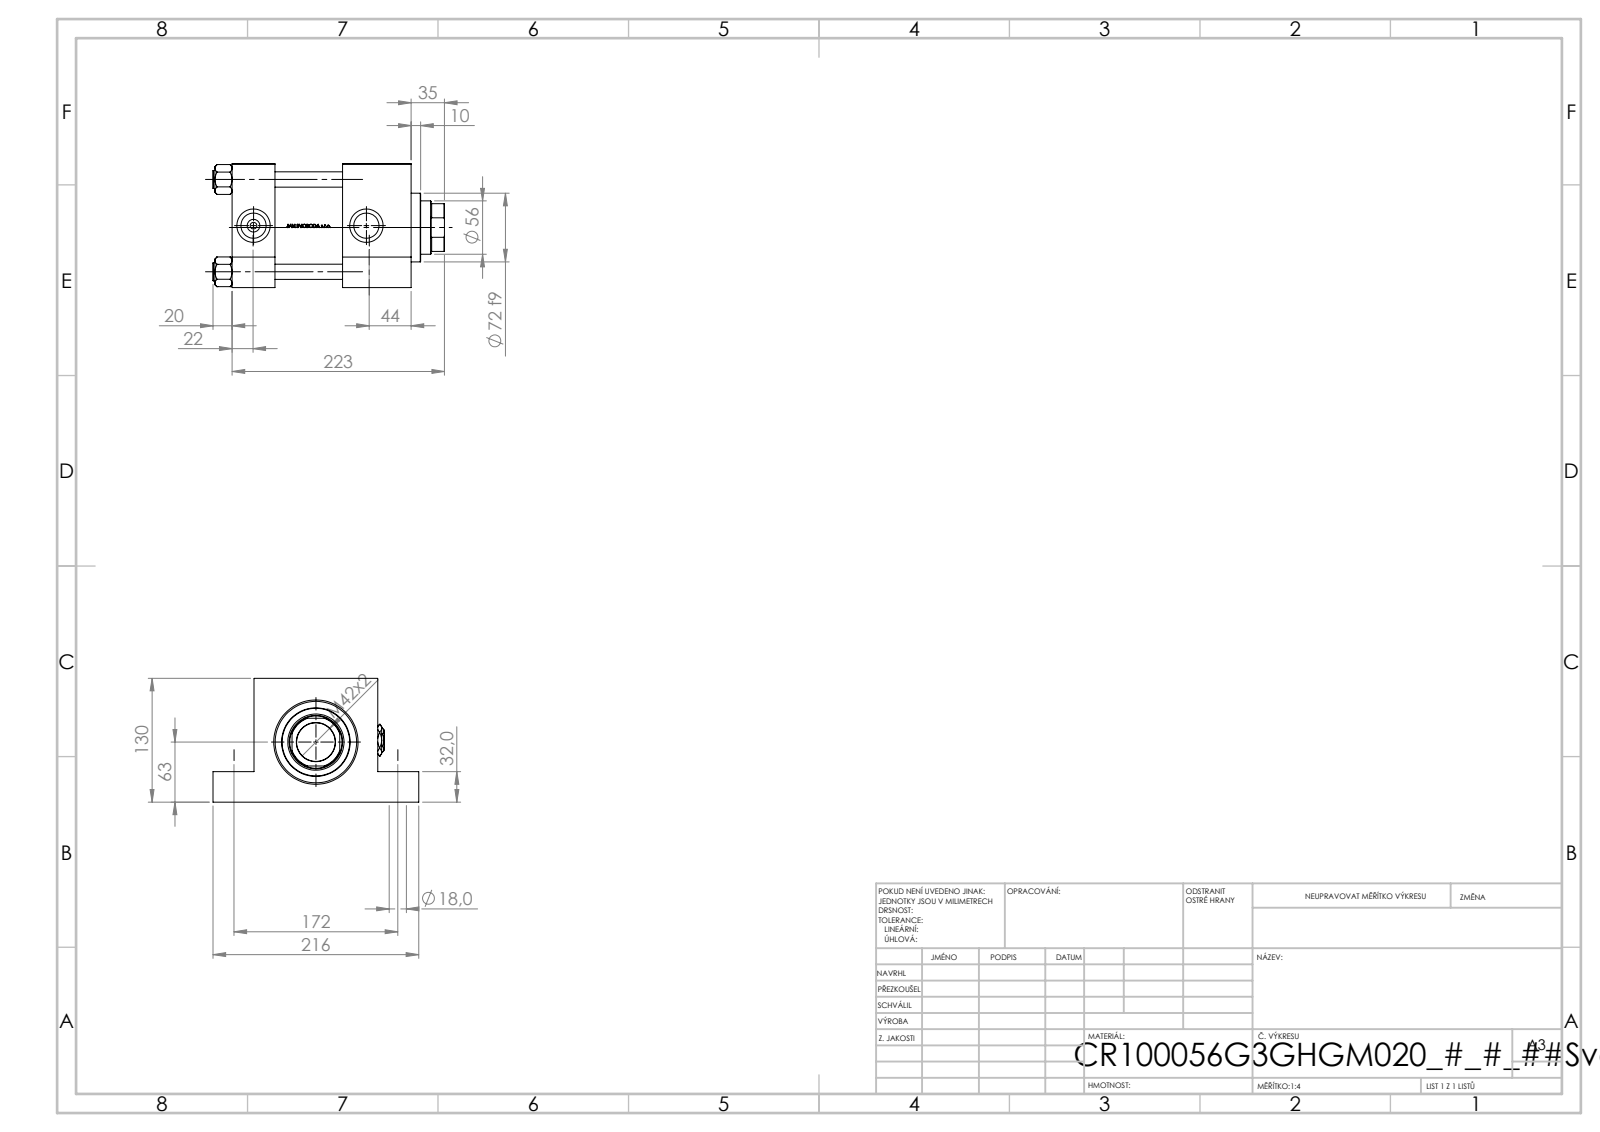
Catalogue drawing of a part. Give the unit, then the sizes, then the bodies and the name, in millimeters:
Units: millimetres
Overall size (bounding box): 243 × 216 × 130
Round holes (diameter × count): ⌀16 ×4, ⌀18 ×4, ⌀7 ×2, ⌀26.44 ×2, ⌀35 ×2, ⌀40.5 ×1, ⌀56 ×1, ⌀59 ×1, ⌀76 ×1, ⌀85.5 ×1, ⌀100 ×1
Round bosses / shafts (diameter × count): ⌀19 ×4, ⌀106 ×1, ⌀72 ×1
Partial cylindrical surfaces — rounded edges, fillets, slot ends (radius × count): R27 ×1
Main face-to-face distances: 130, 45, 188, 143, 116, 71, 72, 32, 98, 43
Hole centre spacings: 96.9, 67.12, 69.95, 122, 137.04, 172, 210.87, 118.5
Volume: 2 774 000 mm³ · Surface area: 370 926 mm²
Bodies: 13 solids, 1231 faces (525 planar, 132 cylindrical, 574 other)
Part name (STEP PRODUCT): V215CR_G_Body; Zatka_pro_OIL_PORT; V215CR_VCP_G; V215CR_G_TYCINKA (+2 more)
STEP written by: SolidWorks 2019 (CONFIG_CONTROL_DESIGN)
